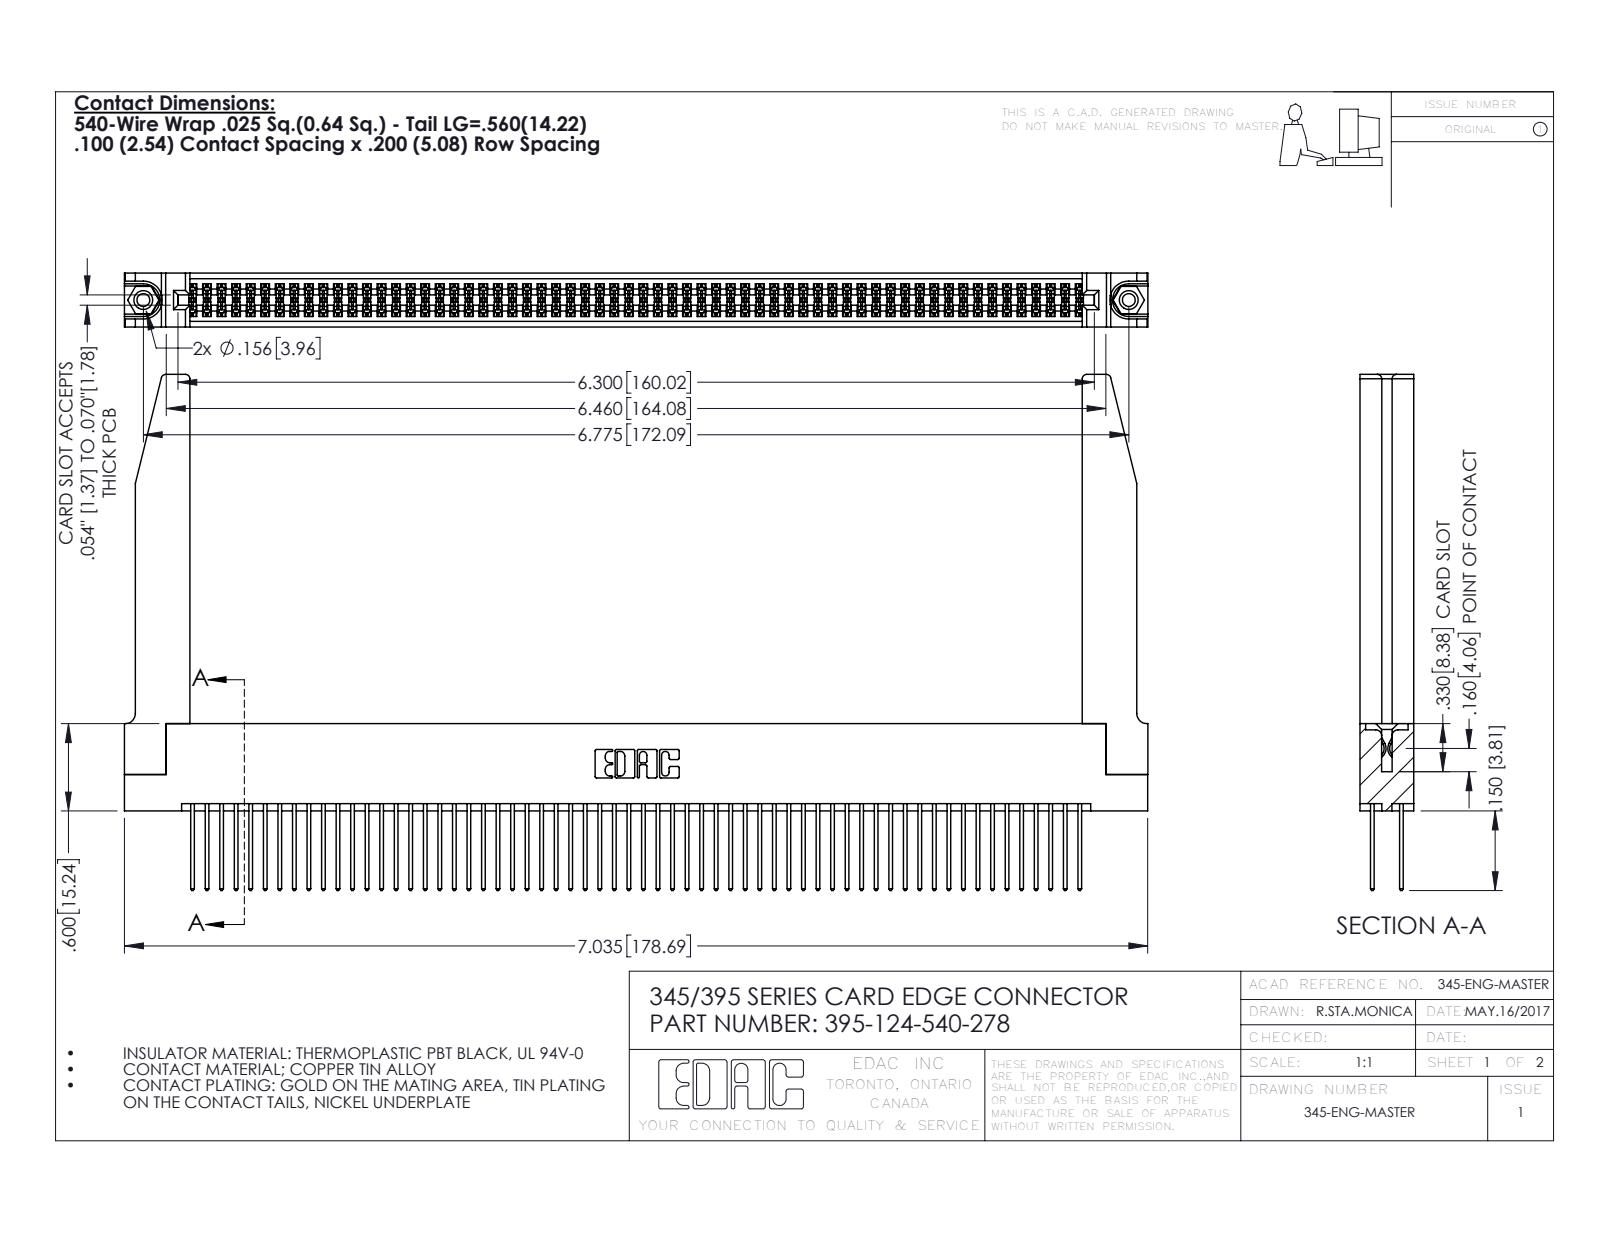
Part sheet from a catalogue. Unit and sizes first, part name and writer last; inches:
Units: inches
Overall size (bounding box): 7.036 × 3.547 × 0.37
Round holes (diameter × count): ⌀0.089 ×2, ⌀0.125 ×2, ⌀0.156 ×2, ⌀0.064 ×1
Round bosses / shafts (diameter × count): ⌀0.155 ×2
Partial cylindrical surfaces — rounded edges, fillets, slot ends (radius × count): R0.006 ×186, R0.01 ×124, R0.01 ×22, R0.03 ×8, R0.007 ×6, R0.031 ×6, R0.026 ×3, R0.014 ×2
Main face-to-face distances: 0.072, 0.298, 0.37, 0.2, 0.098, 0.272, 0.025, 0.225, 0.175, 0.148
Hole centre spacings: 0.27, 6.539, 6.775
Volume: 1.574 in³ · Surface area: 55.86 in²
Bodies: 129 solids, 6560 faces (4314 planar, 2194 cylindrical, 52 other)
Part name (STEP PRODUCT): 345-292-001_345-293-140; 345-250-001_345-250-001-102; 395-124-540-278; 345-220-078_345-220-078 (+1 more)
STEP written by: SolidWorks 2016 (CONFIG_CONTROL_DESIGN)
